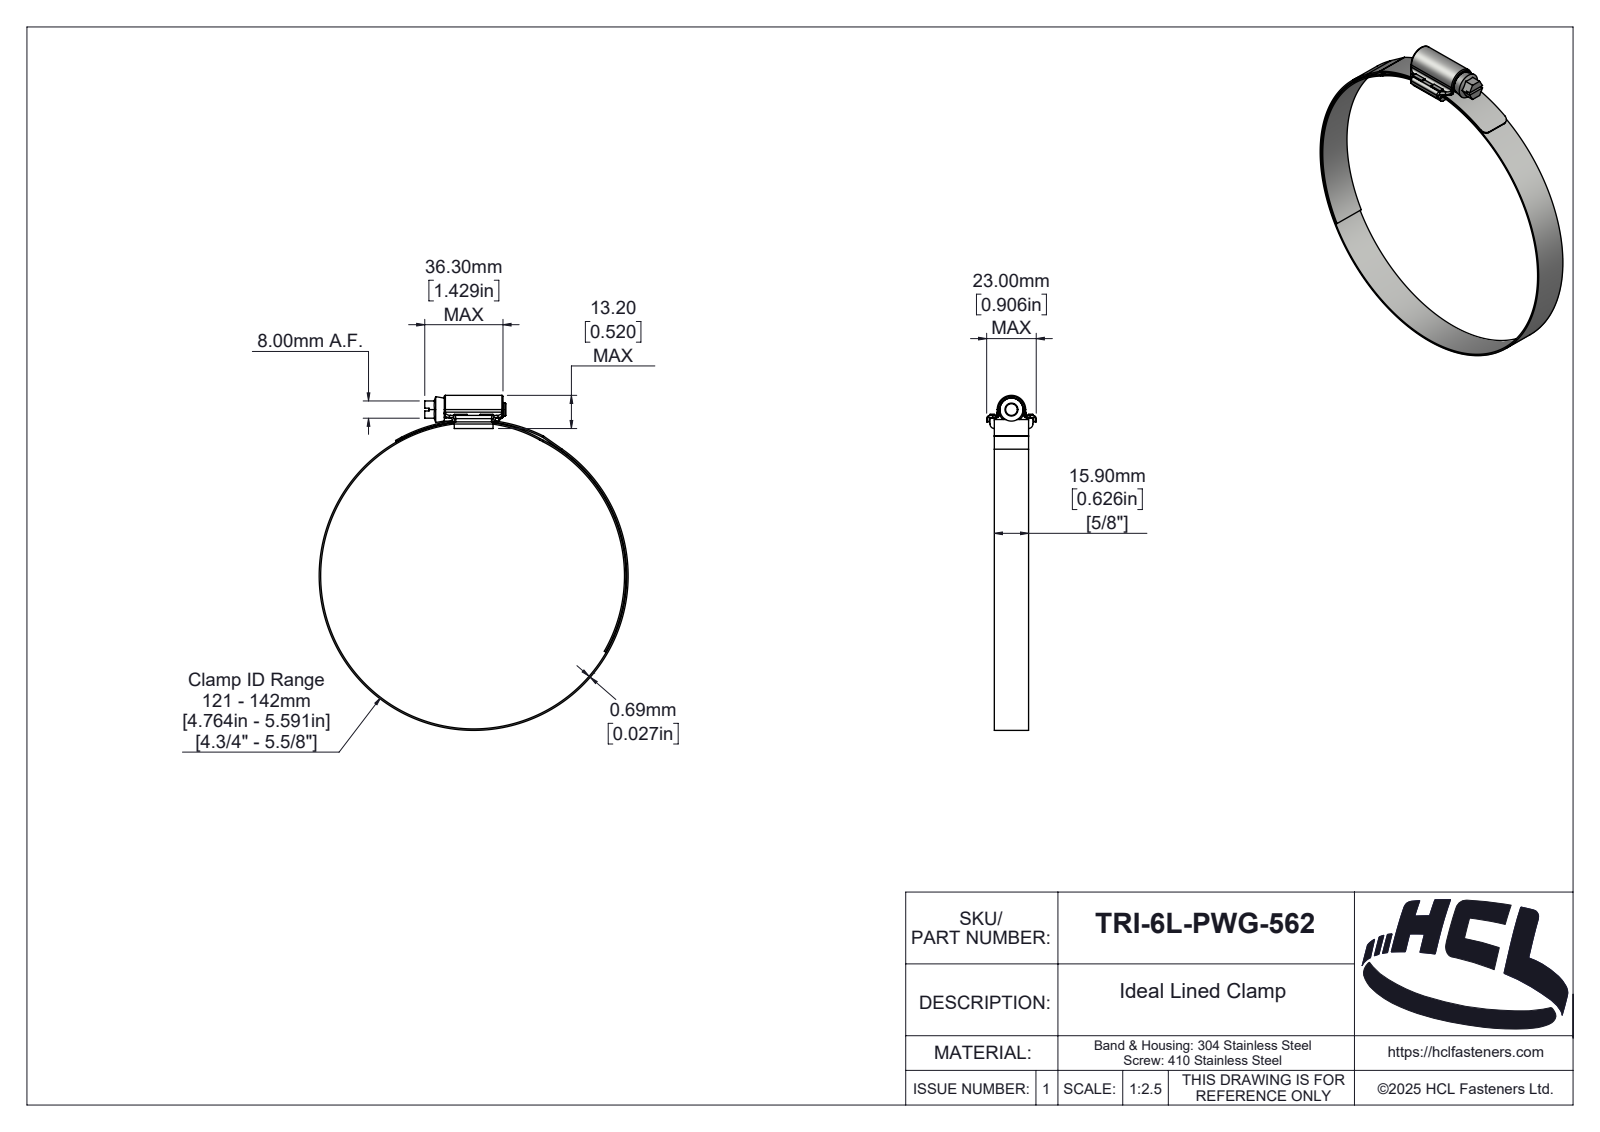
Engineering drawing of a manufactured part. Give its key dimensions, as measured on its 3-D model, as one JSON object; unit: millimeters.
{"part_name": "TRI-6L-PWG-562", "step_written_by": "SolidWorks 2025 (AUTOMOTIVE_DESIGN)", "units": "millimeters", "bodies": {"solids": 4, "faces": 268, "planar": 87, "cylindrical": 102, "other": 79}, "overall_size": [155.39, 143.38, 23], "volume_mm3": 12149, "surface_area_mm2": 25641, "round_holes": [[142, 1]], "round_bosses_or_shafts": [[143.38, 1], [10.7, 1], [6, 1]], "partial_cylinders_radius": [[1, 14], [0.5, 4], [1.5, 4], [2, 3], [0.1, 2], [2.1, 2], [3, 2], [0.46, 1]], "face_to_face_distances": [15.9, 2, 17.9, 0.69, 4.9, 1.2, 4.55, 3.35, 15.35, 2.55]}
